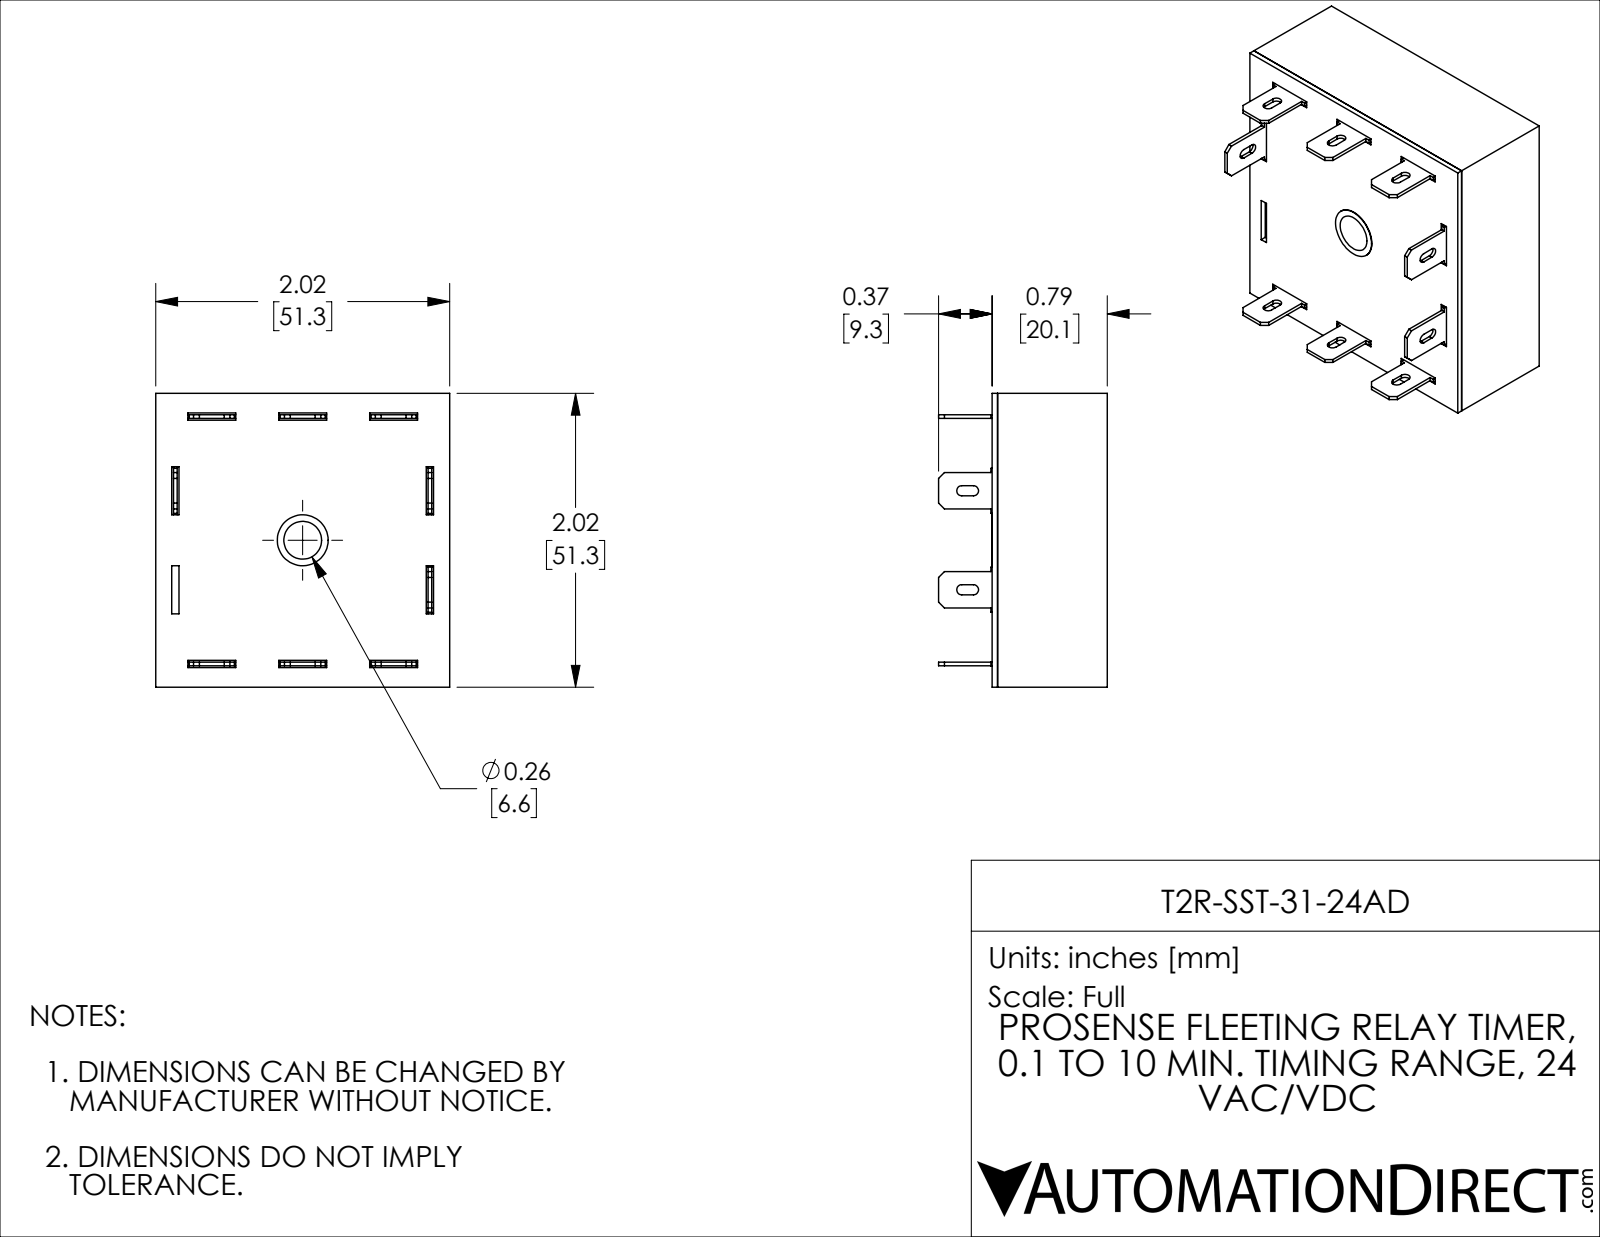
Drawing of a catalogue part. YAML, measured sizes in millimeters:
part_name: "T2R-SST-31-24AD"
step_written_by: "SolidWorks 2021 (CONFIG_CONTROL_DESIGN)"
units: millimeters
bodies: {solids: 11, faces: 280, planar: 256, cylindrical: 22, other: 2}
overall_size: [51.31, 51.31, 29.46]
volume: 11178
surface_area: 23301
round_holes:
  - {diameter: 8.89, count: 1}
partial_cylinders:
  - {radius: 0.89, count: 10}
face_to_face_distances: [1.14, 50.16, 19.15, 20.12, 0.97, 18.01, 18.98, 51.3, 3.74, 47.56]
